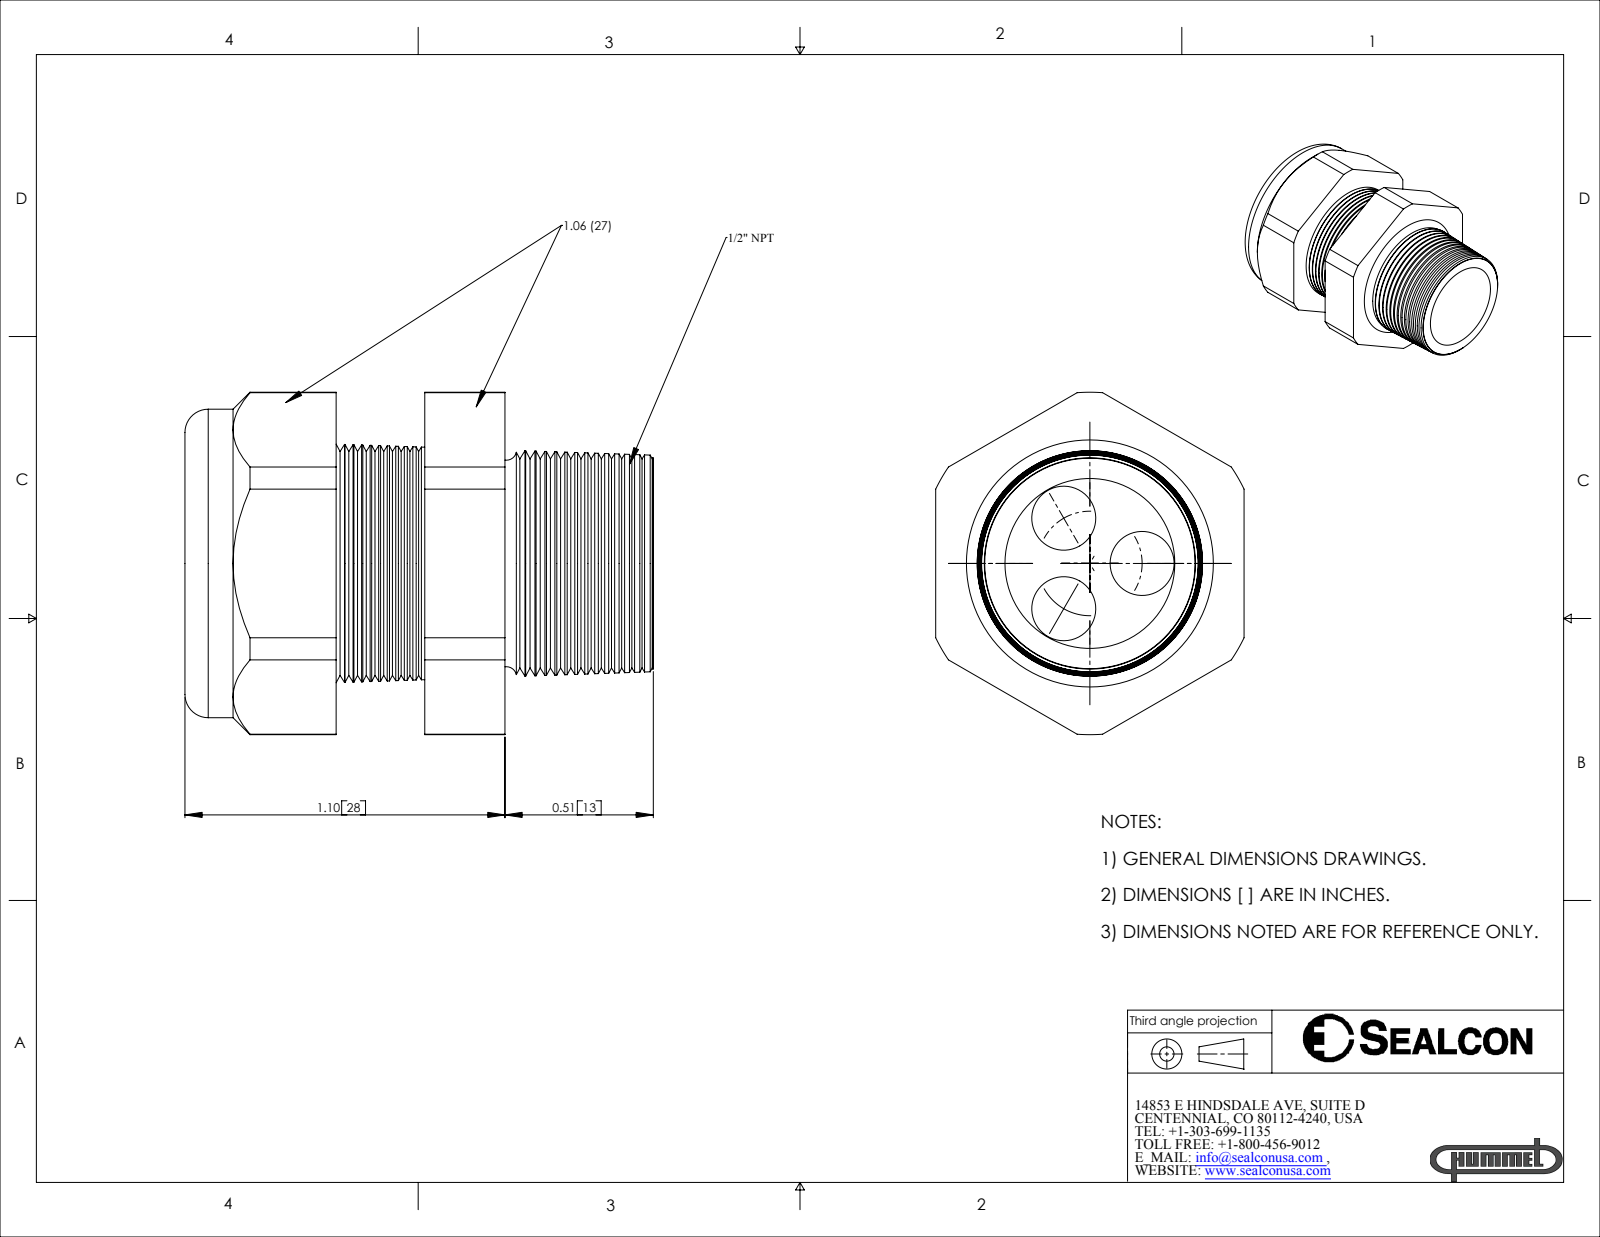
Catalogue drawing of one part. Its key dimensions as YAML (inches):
part_name: "CD16N7-GY"
step_written_by: "SolidWorks 2007 (CONFIG_CONTROL_DESIGN)"
units: inches
bodies: {solids: 2, faces: 204, planar: 20, cylindrical: 26, other: 158}
overall_size: [1.61, 1.177, 1.06]
volume: 0.726
surface_area: 13.07
round_holes:
  - {diameter: 0.22, count: 3}
  - {diameter: 0.58, count: 1}
  - {diameter: 0.6, count: 1}
round_bosses_or_shafts:
  - {diameter: 1.06, count: 1}
partial_cylinders:
  - {radius: 0.588, count: 1}
face_to_face_distances: [1.06, 0.305, 0.58, 0.276, 0.52, 0.824, 1.1, 0.35, 0.17, 0.474]
hole_center_spacings: [0.18, 0.311]
